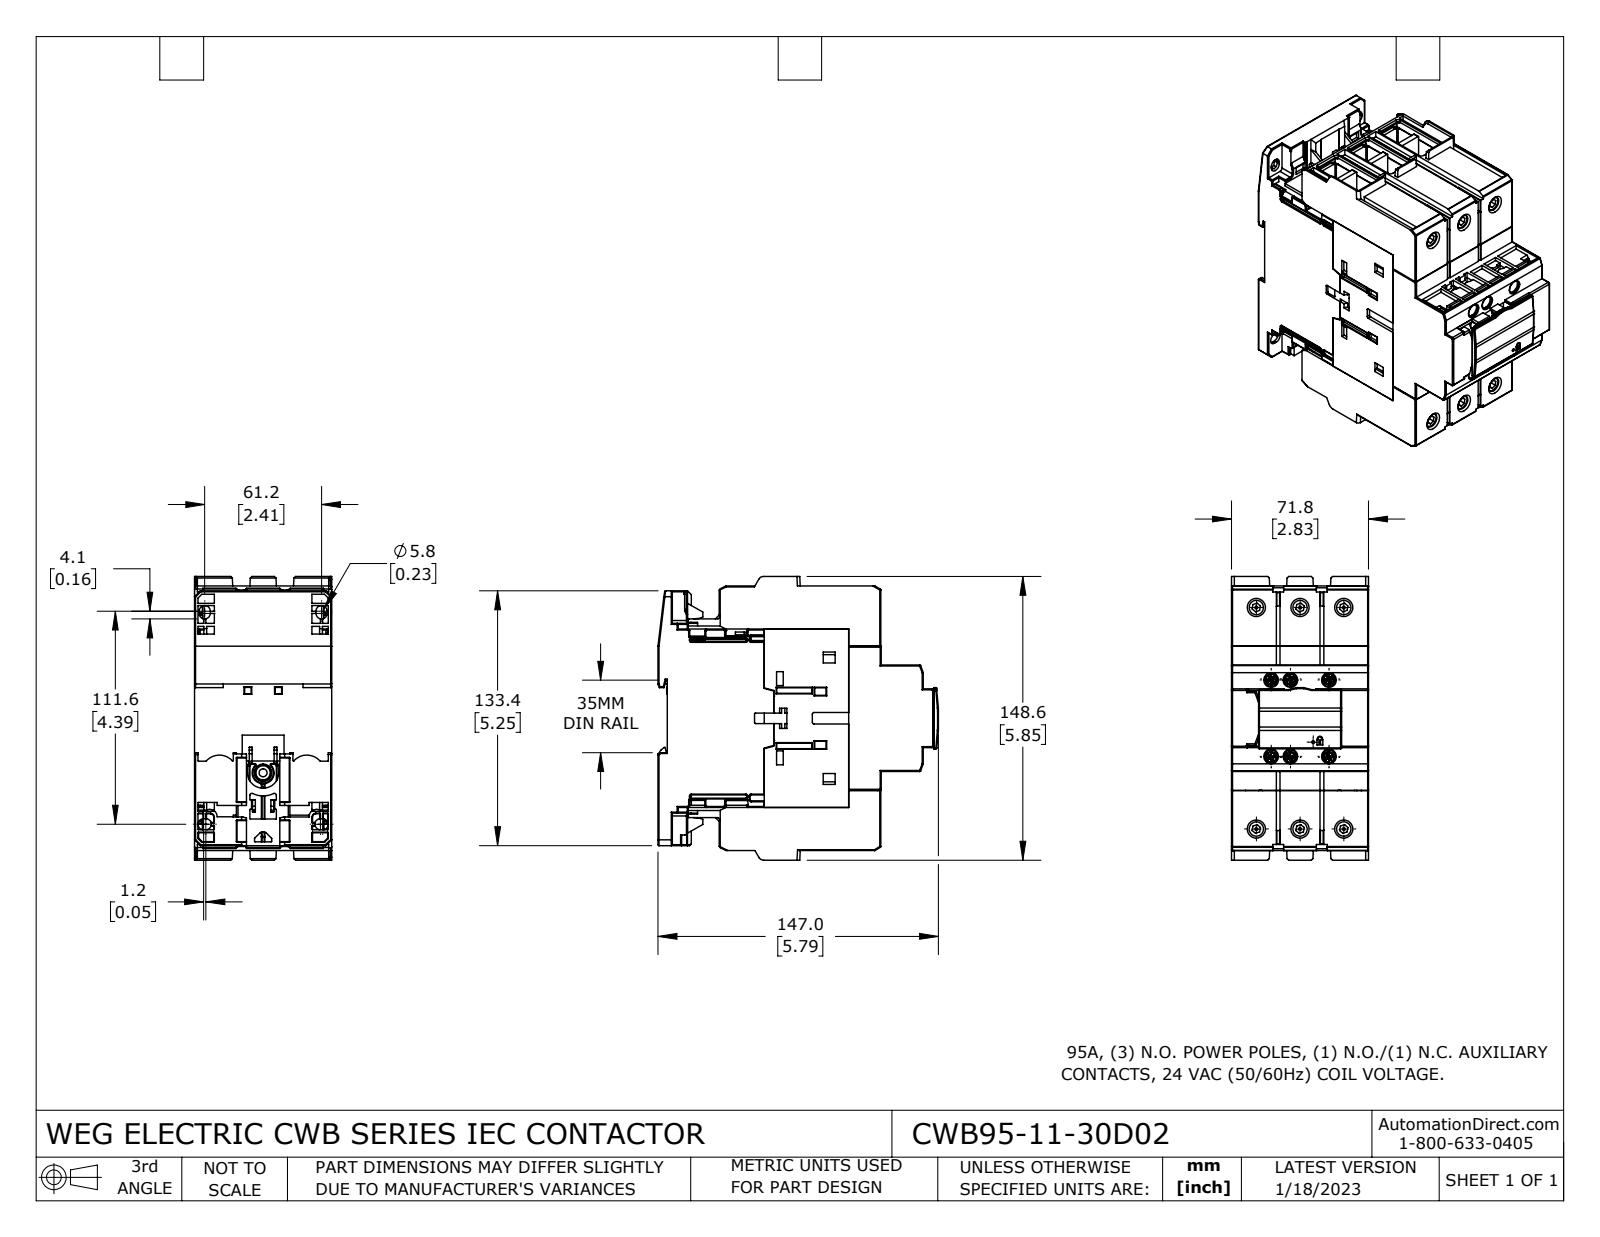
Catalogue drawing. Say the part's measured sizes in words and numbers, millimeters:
The part is named "CWB95-11-30D02". Its 3-D file was written by "SolidWorks 2021 (CONFIG_CONTROL_DESIGN)". It is 39 solids with 5736 faces: 3711 planar, 1453 cylindrical and 572 other. Overall it measures 148.6 by 146.9 by 71.8 millimeters. Its volume is 904 400 cubic millimeters and its surface area 294 600 square millimeters. Round holes: 10 of diameter 4.2, 8 of diameter 3.3, 7 of diameter 7, 6 of diameter 2.9, 6 of diameter 3.1, 6 of diameter 6.7, 6 of diameter 7.5, 6 of diameter 9.5, 4 of diameter 7.3, 1 of diameter 1.5, 1 of diameter 8.5. Round bosses or shafts: 6 of diameter 9.3, 6 of diameter 8, 6 of diameter 4.3, 6 of diameter 3.6, 1 of diameter 7. Partial cylindrical surfaces (rounded edges, fillets, slot ends): 315 of radius 0.5, 127 of radius 0.3, 113 of radius 0.4, 63 of radius 0.2, 49 of radius 1, 36 of radius 0.6, 20 of radius 1.5, 14 of radius 0.8. The main face-to-face distances are 1.5, 22.9, 71.8, 3, 23.7, 46.6, 25.2, 45.1, 48.1, 22.2. The hole center spacings are 22.9, 30.3, 63.7, 10.1, 16.9, 18.2, 20.2, 20.2.
